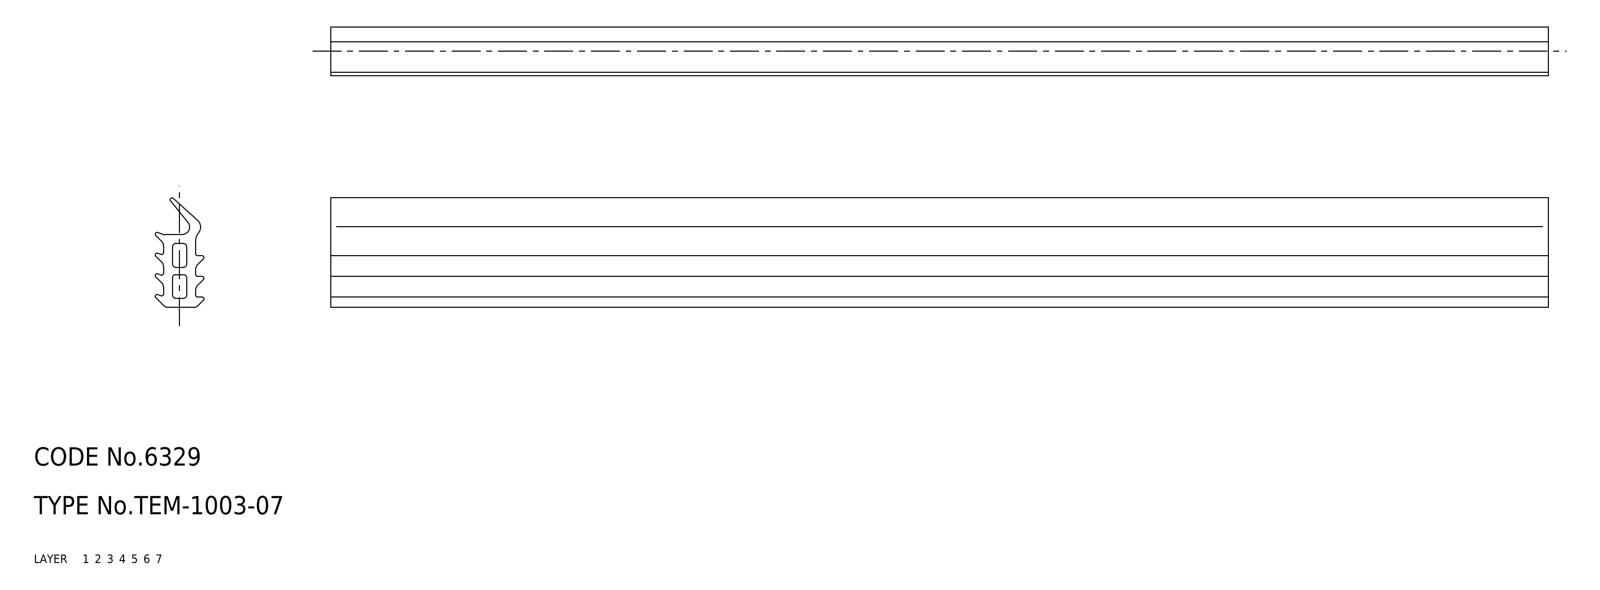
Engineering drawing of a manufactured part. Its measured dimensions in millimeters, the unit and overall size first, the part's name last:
Units: millimetres
Overall size (bounding box): 200 × 18 × 8
Volume: 12 972 mm³ · Surface area: 16 936 mm²
Bodies: 1 solid, 68 faces (0 planar, 0 cylindrical, 68 other)
Part name (STEP PRODUCT): gasket
STEP written by: CADfix (AUTOMOTIVE_DESIGN)
